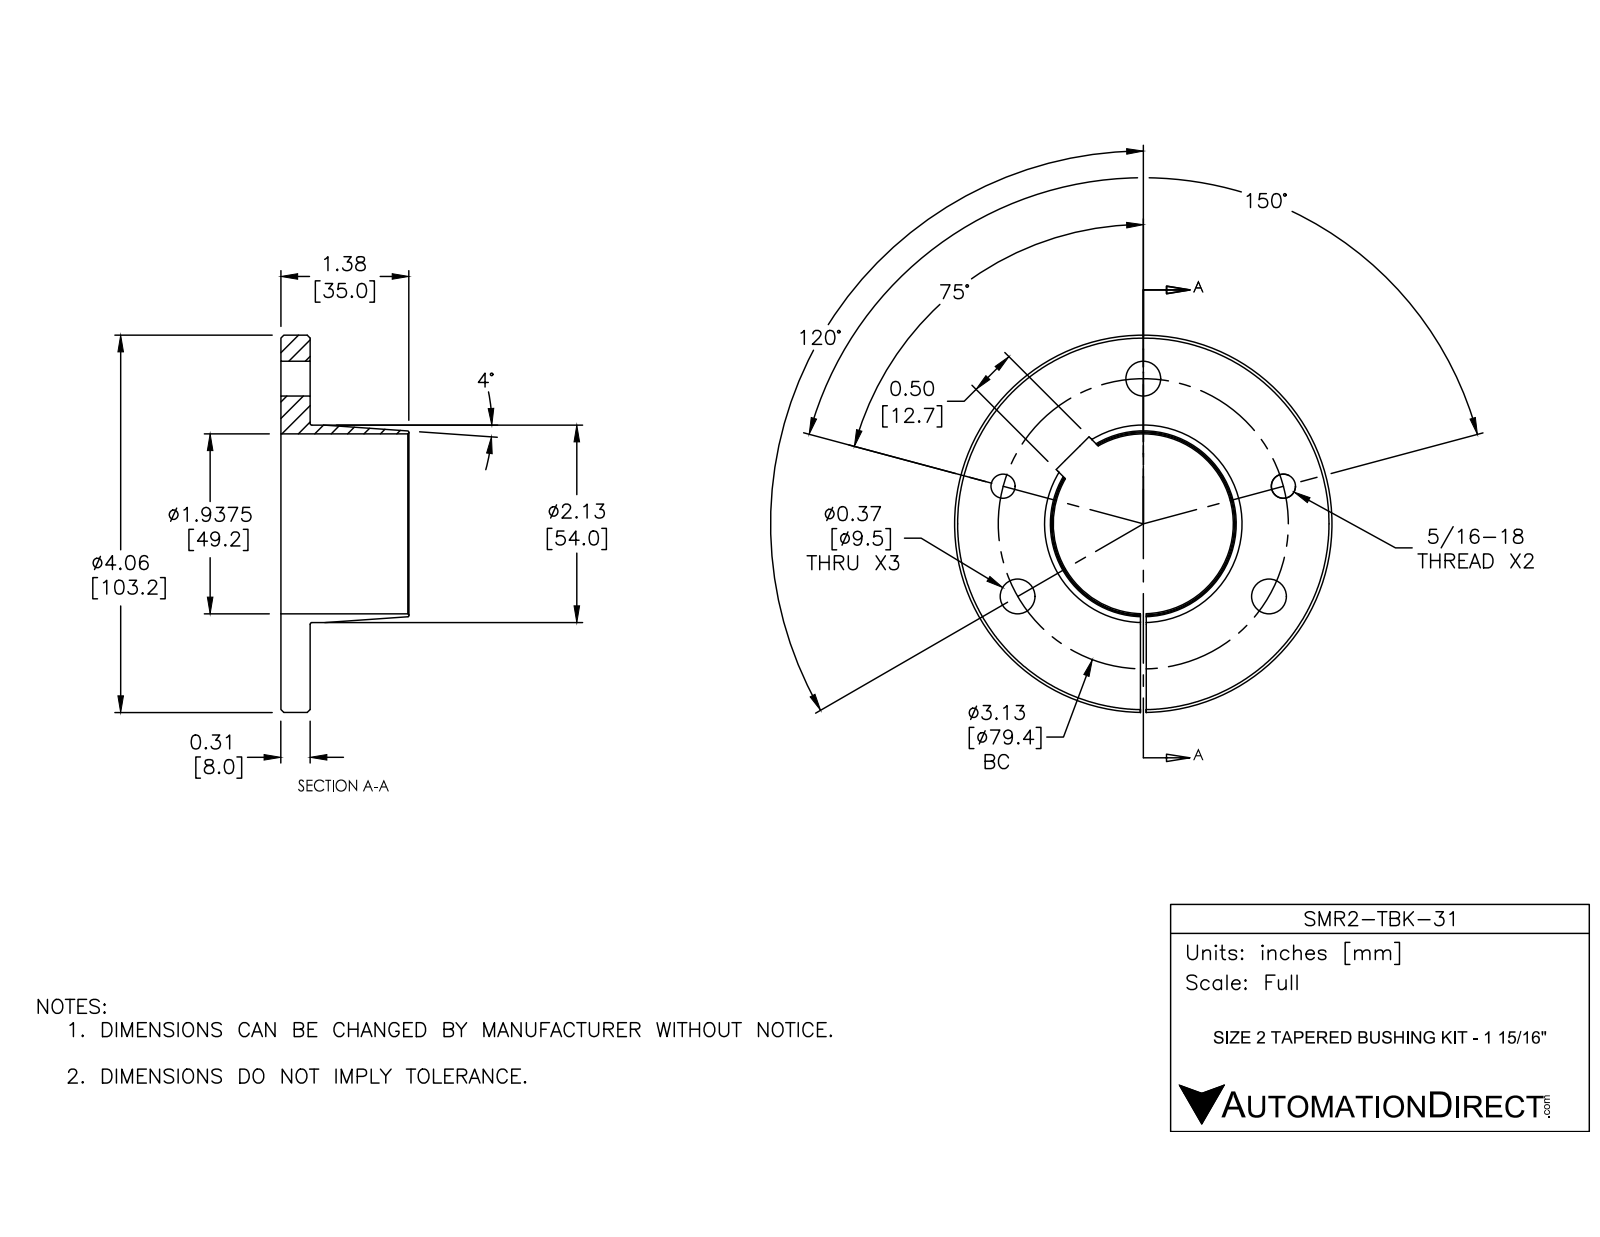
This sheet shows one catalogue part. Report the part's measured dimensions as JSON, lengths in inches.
{"part_name": "SMR2-TBK-31", "step_written_by": "SolidWorks 2016 (AUTOMOTIVE_DESIGN)", "units": "inches", "bodies": {"solids": 1, "faces": 124, "planar": 18, "cylindrical": 79, "other": 27}, "overall_size": [4.063, 4.062, 1.378], "volume_in3": 5.392, "surface_area_in2": 42.62, "round_holes": [[0.374, 3], [0.32, 2], [0.26, 1], [1.313, 1], [1.328, 1]], "round_bosses_or_shafts": [[4.063, 1], [2.126, 1]], "partial_cylinders_radius": [[0.13, 2], [0.197, 2]], "face_to_face_distances": [0.315, 1.378, 1.063, 0.063, 1.616, 0.094, 0.406, 0.313, 0.5, 0.354], "hole_center_spacings": [1.563, 2.707, 1.196, 1.563, 1.563, 1.903, 1.904, 3.02]}
